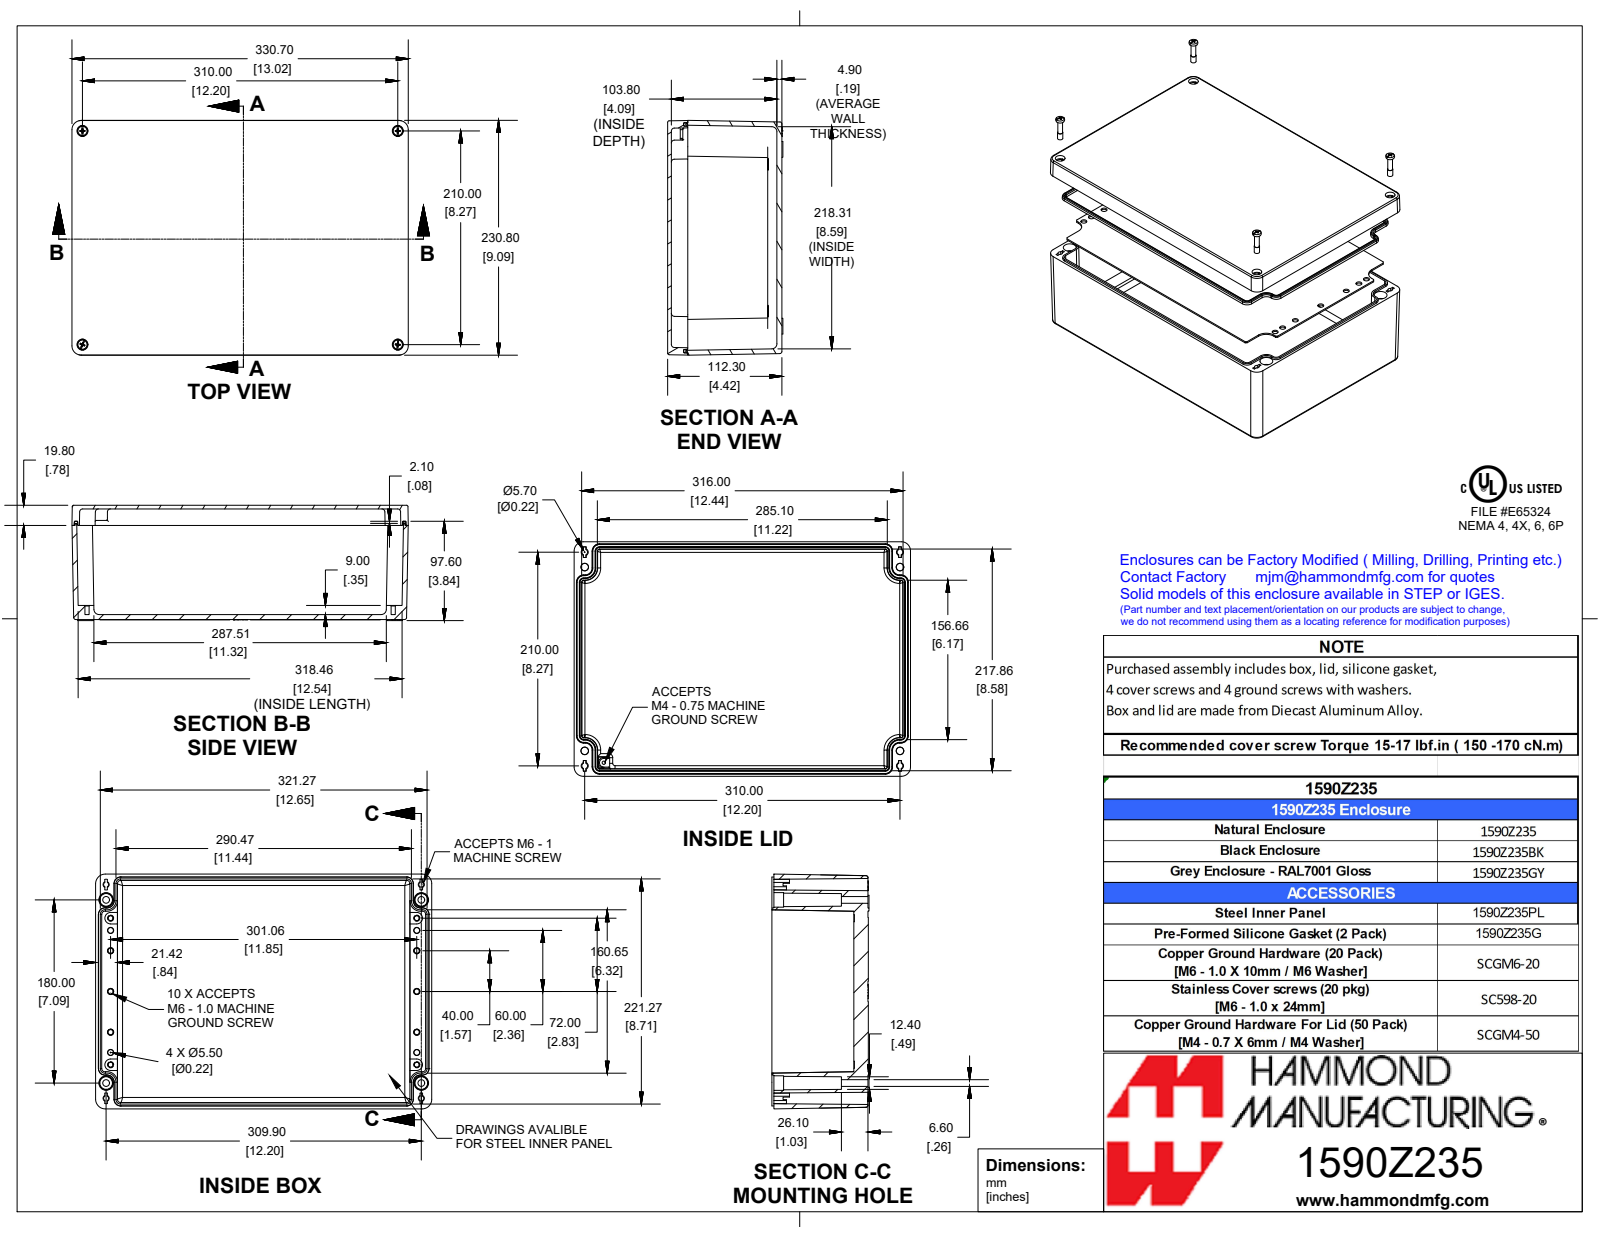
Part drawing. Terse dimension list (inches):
name: 1590Z235
written by: SolidWorks 2019 (CONFIG_CONTROL_DESIGN)
unit: in
bodies: 8 solids, 1112 faces (529 planar, 204 cylindrical, 379 other)
size: 13.02 × 9.087 × 4.461
volume: 91.92 in³; area: 1 120 in²
holes: 14× ⌀0.257, 8× ⌀0.194, 4× ⌀0.217, 4× ⌀0.26, 4× ⌀0.425, 4× ⌀0.563, 2× ⌀0.194, 1× ⌀0.128
bosses: 4× ⌀0.231, 4× ⌀0.208
rounds: 23× R0.039, 20× R0.059, 17× R0.02, 10× R0.118, 4× R0.079, 4× R0.097, 4× R0.112, 4× R0.138
face distances: 3.874, 0.547, 4.421, 0.079, 0.626, 3.795, 3.654, 3.732, 4.28, 0.142
hole spacings: 11.853, 11.86, 1.575, 2.362, 2.835, 0.472, 0.591, 0.73
